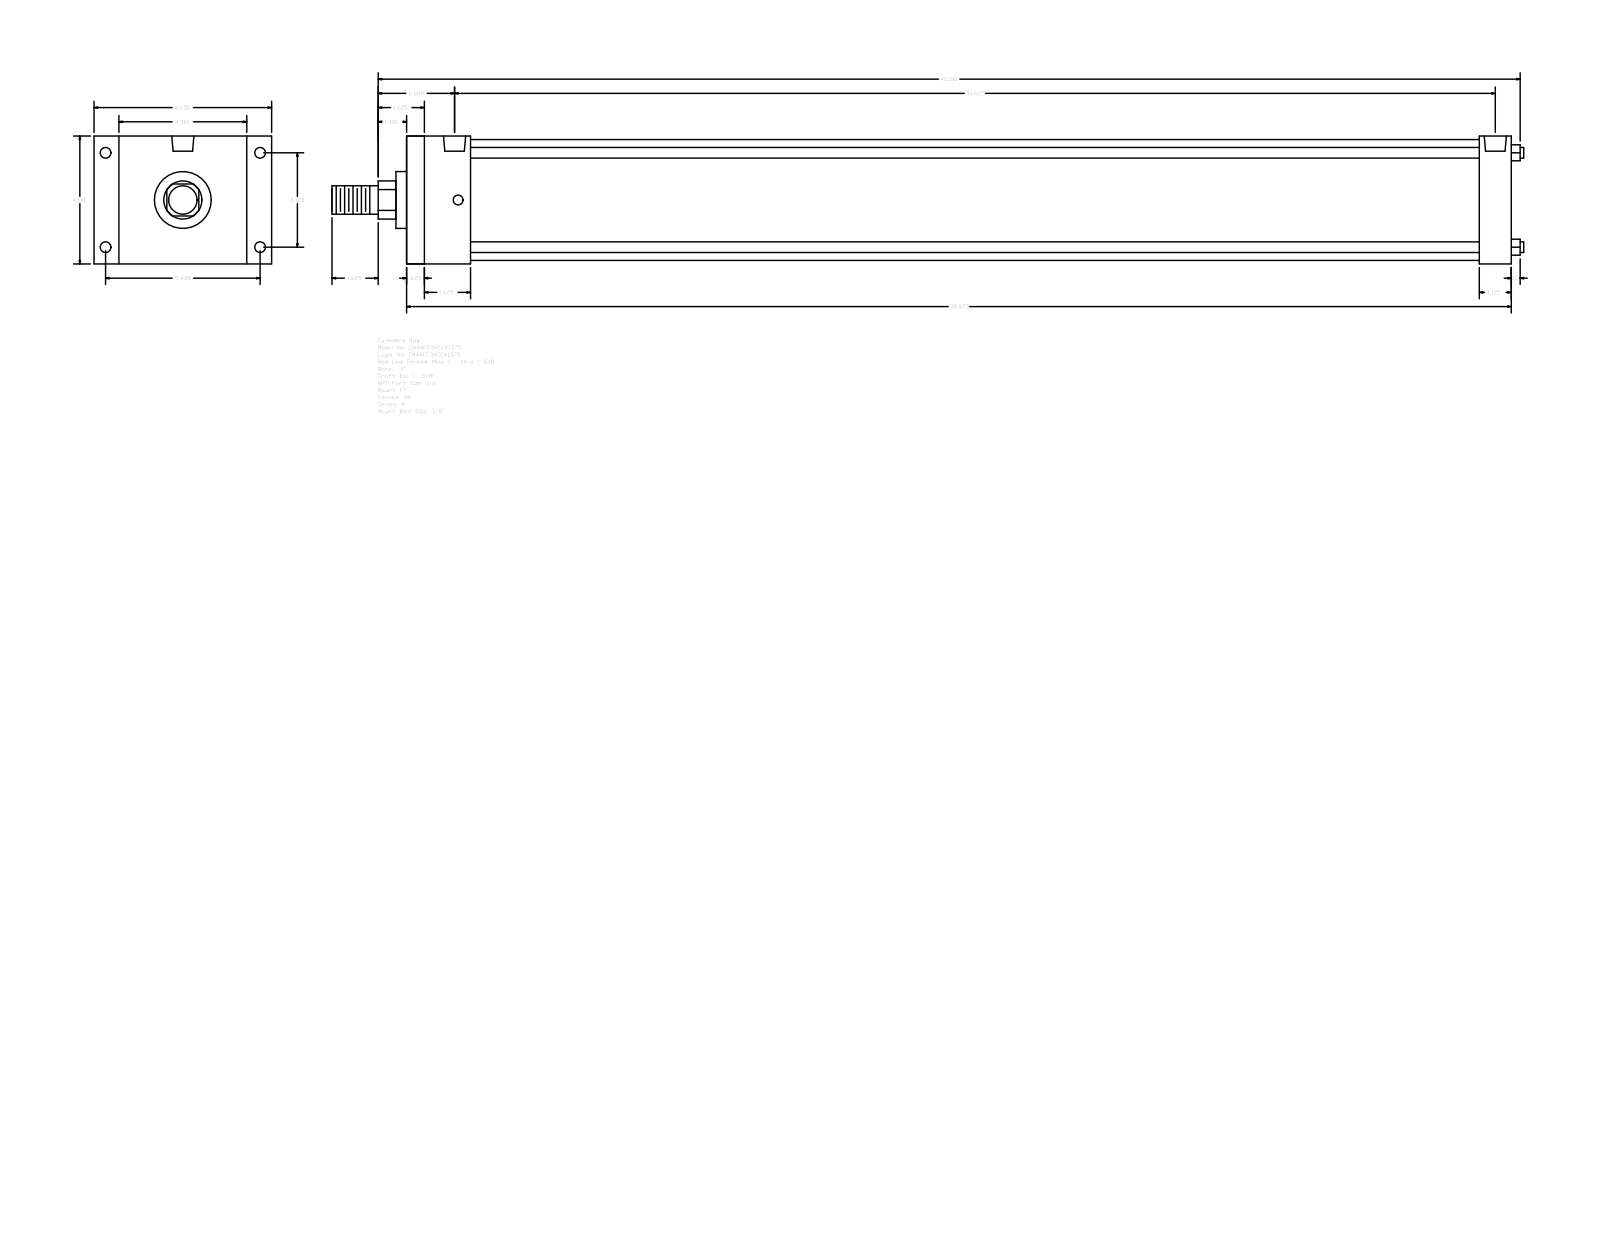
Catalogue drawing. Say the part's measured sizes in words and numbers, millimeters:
The part is named "A_FF__0400_1.375". Its 3-D file was written by "GSSL Pune (CONFIG_CONTROL_DESIGN)". It is 0 solids with 92 faces: 64 planar, 28 cylindrical and 0 other. Overall it measures 1065.21 by 158.75 by 114.3 millimeters. Round holes: 4 of diameter 8.73, 4 of diameter 9.53, 2 of diameter 19.77. Round bosses or shafts: 4 of diameter 9.53, 1 of diameter 107.95, 1 of diameter 50.8, 1 of diameter 34.92, 1 of diameter 25.4. Partial cylindrical surfaces (rounded edges, fillets, slot ends): 1 of radius 17.06. The main face-to-face distances are 114.3, 987.43, 15.87, 971.56, 57.15, 28.58, 22.23, 136.53, 958.85, 942.98. The hole center spacings are 3.18, 84.32, 138.12, 161.82, 923.92, 927.1, 930.28.
